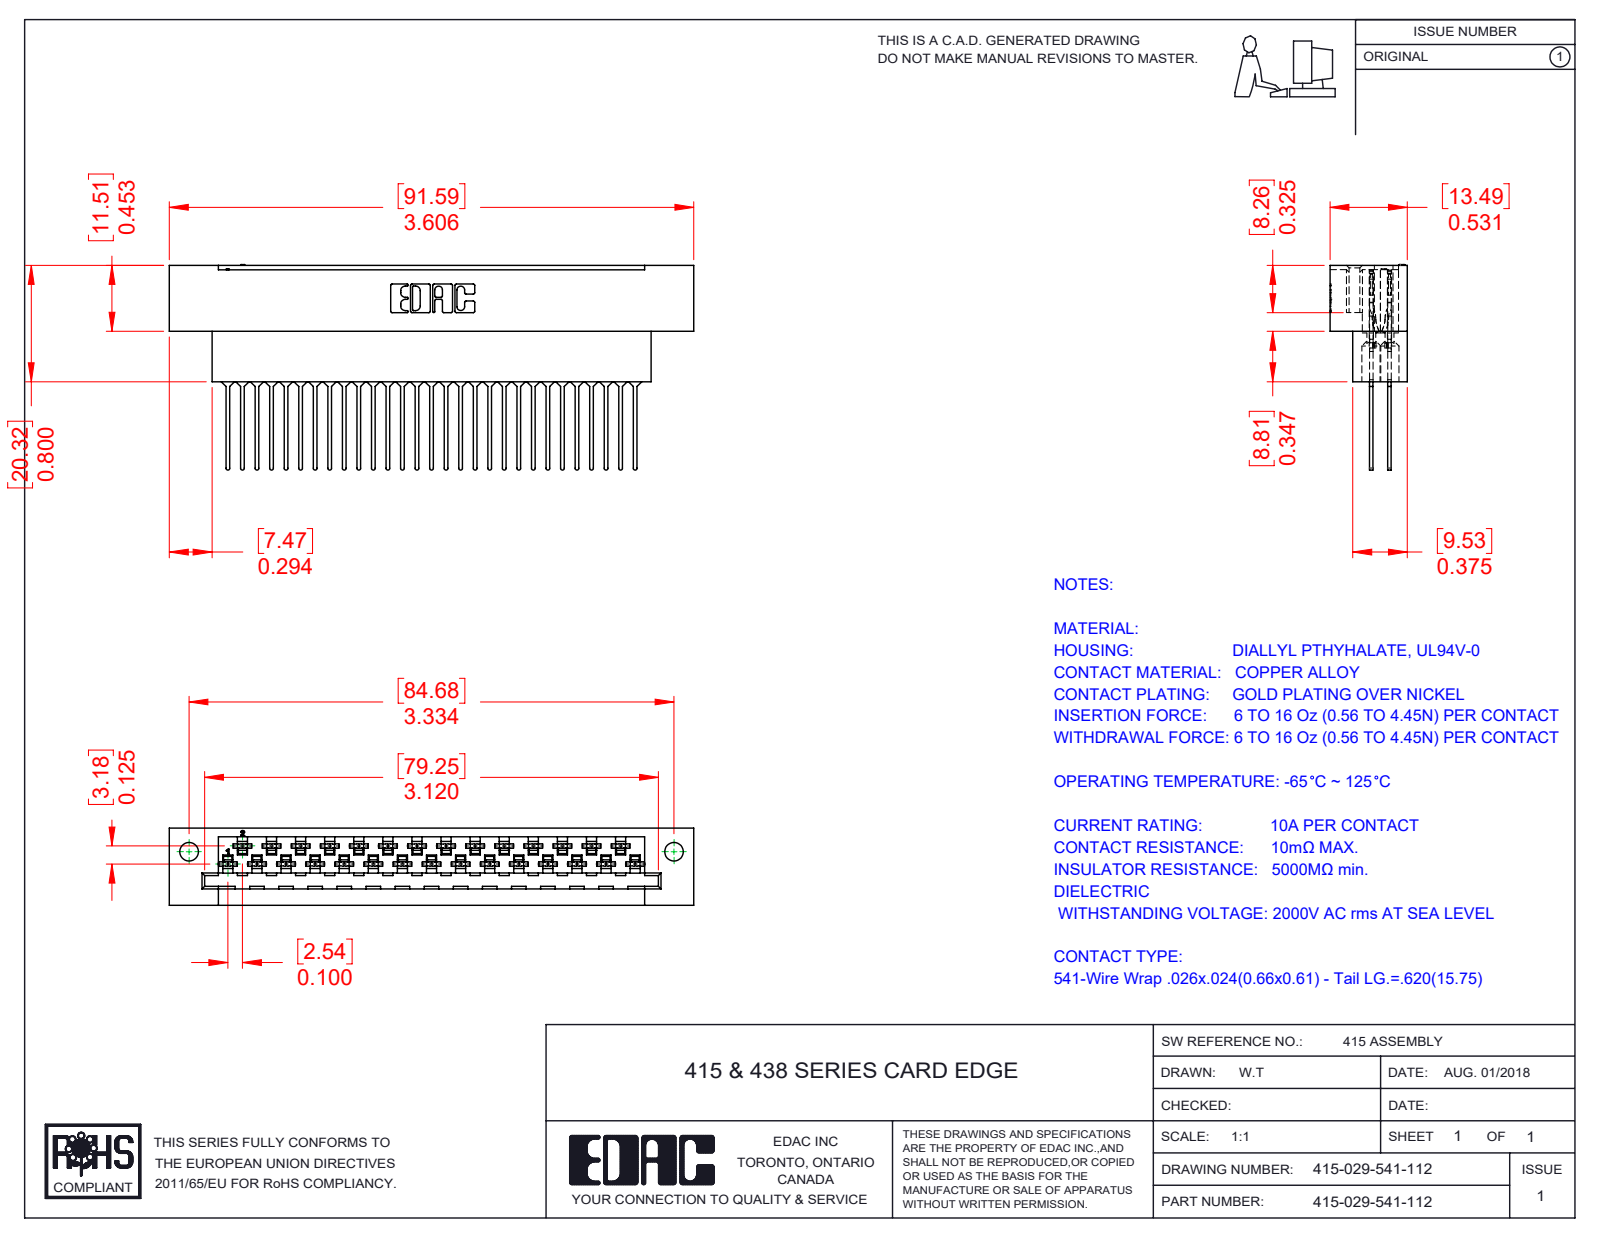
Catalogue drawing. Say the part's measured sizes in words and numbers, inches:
The part is named "516-290-001_541; 415-210-001_415-210-029-112; 415-029-541-112". Its 3-D file was written by "SolidWorks 2016 (CONFIG_CONTROL_DESIGN)". It is 30 solids with 2986 faces: 1905 planar, 798 cylindrical and 283 other. Overall it measures 3.606 by 1.411 by 0.531 inches. Its volume is 0.946 cubic inches and its surface area 30.12 square inches. Round holes: 29 of diameter 0.05, 29 of diameter 0.13, 2 of diameter 0.128. Partial cylindrical surfaces (rounded edges, fillets, slot ends): 116 of radius 0.012, 116 of radius 0.022, 58 of radius 0.007, 58 of radius 0.008, 58 of radius 0.016, 58 of radius 0.08, 29 of radius 0.013, 22 of radius 0.01. The main face-to-face distances are 0.125, 0.024, 0.074, 0.531, 0.295, 0.05, 0.26, 0.271, 0.236, 0.111. The hole center spacings are 0.2, 0.4, 0.6, 0.8, 1, 1.2, 1.4, 0.1.
